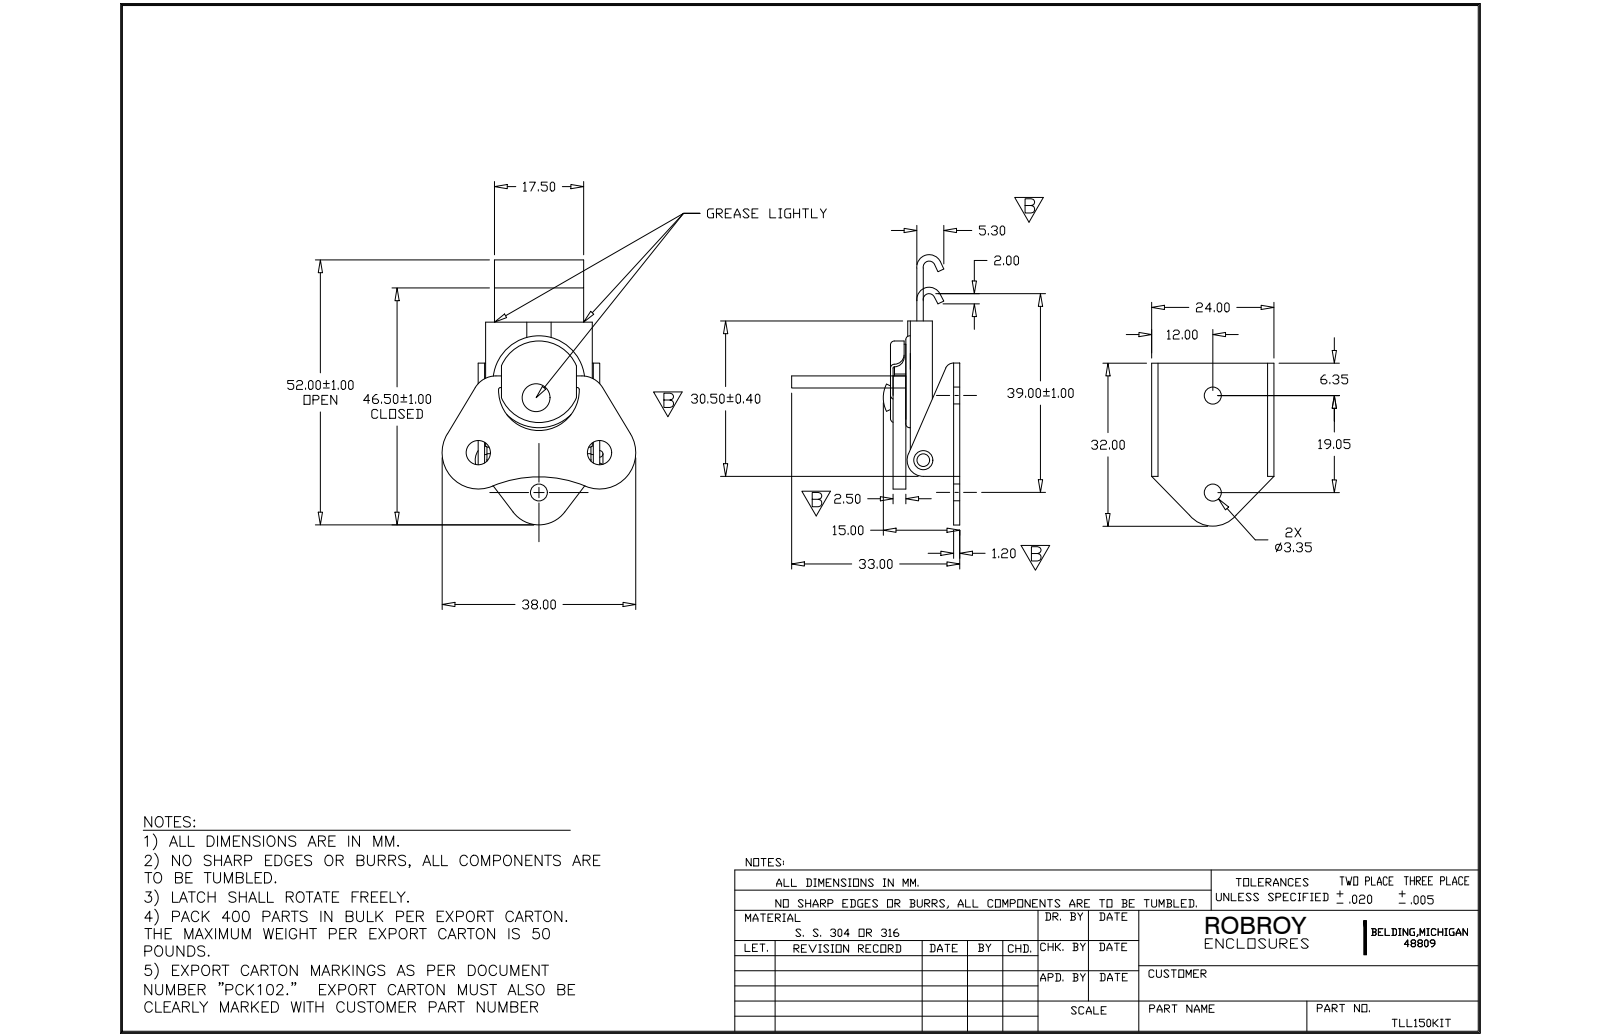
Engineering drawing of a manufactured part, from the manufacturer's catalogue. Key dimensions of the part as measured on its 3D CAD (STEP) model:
Part name (STEP PRODUCT): TLL150KIT
STEP written by: SolidWorks 2018 (AUTOMOTIVE_DESIGN)
Units: inches
Bodies: 16 solids, 225 faces (112 planar, 100 cylindrical, 13 other)
Overall size (bounding box): 2.481 × 1.917 × 1.475
Volume: 0.37 in³ · Surface area: 16.71 in²
Round holes (diameter × count): ⌀0.075 ×2, ⌀0.098 ×2, ⌀0.104 ×2, ⌀0.13 ×2, ⌀0.13 ×2, ⌀0.133 ×2, ⌀0.187 ×2, ⌀0.191 ×2, ⌀0.067 ×1, ⌀0.135 ×1, ⌀0.14 ×1, ⌀0.189 ×1
Round bosses / shafts (diameter × count): ⌀0.283 ×2, ⌀0.14 ×2, ⌀0.125 ×2, ⌀0.66 ×1, ⌀0.582 ×1, ⌀0.525 ×1, ⌀0.286 ×1, ⌀0.213 ×1
Partial cylindrical surfaces — rounded edges, fillets, slot ends (radius × count): R0.015 ×8, R0.06 ×6, R0.011 ×4, R0.02 ×4, R0.055 ×4, R0.07 ×4, R0.079 ×4, R0.05 ×3
Main face-to-face distances: 0.05, 0.082, 0.05, 0.175, 0.093, 0.225, 0.047, 0.132, 0.125, 0.1
Hole centre spacings: 0.75, 0.281, 0.85, 0.125, 0.281, 0.619, 0.652, 0.724
